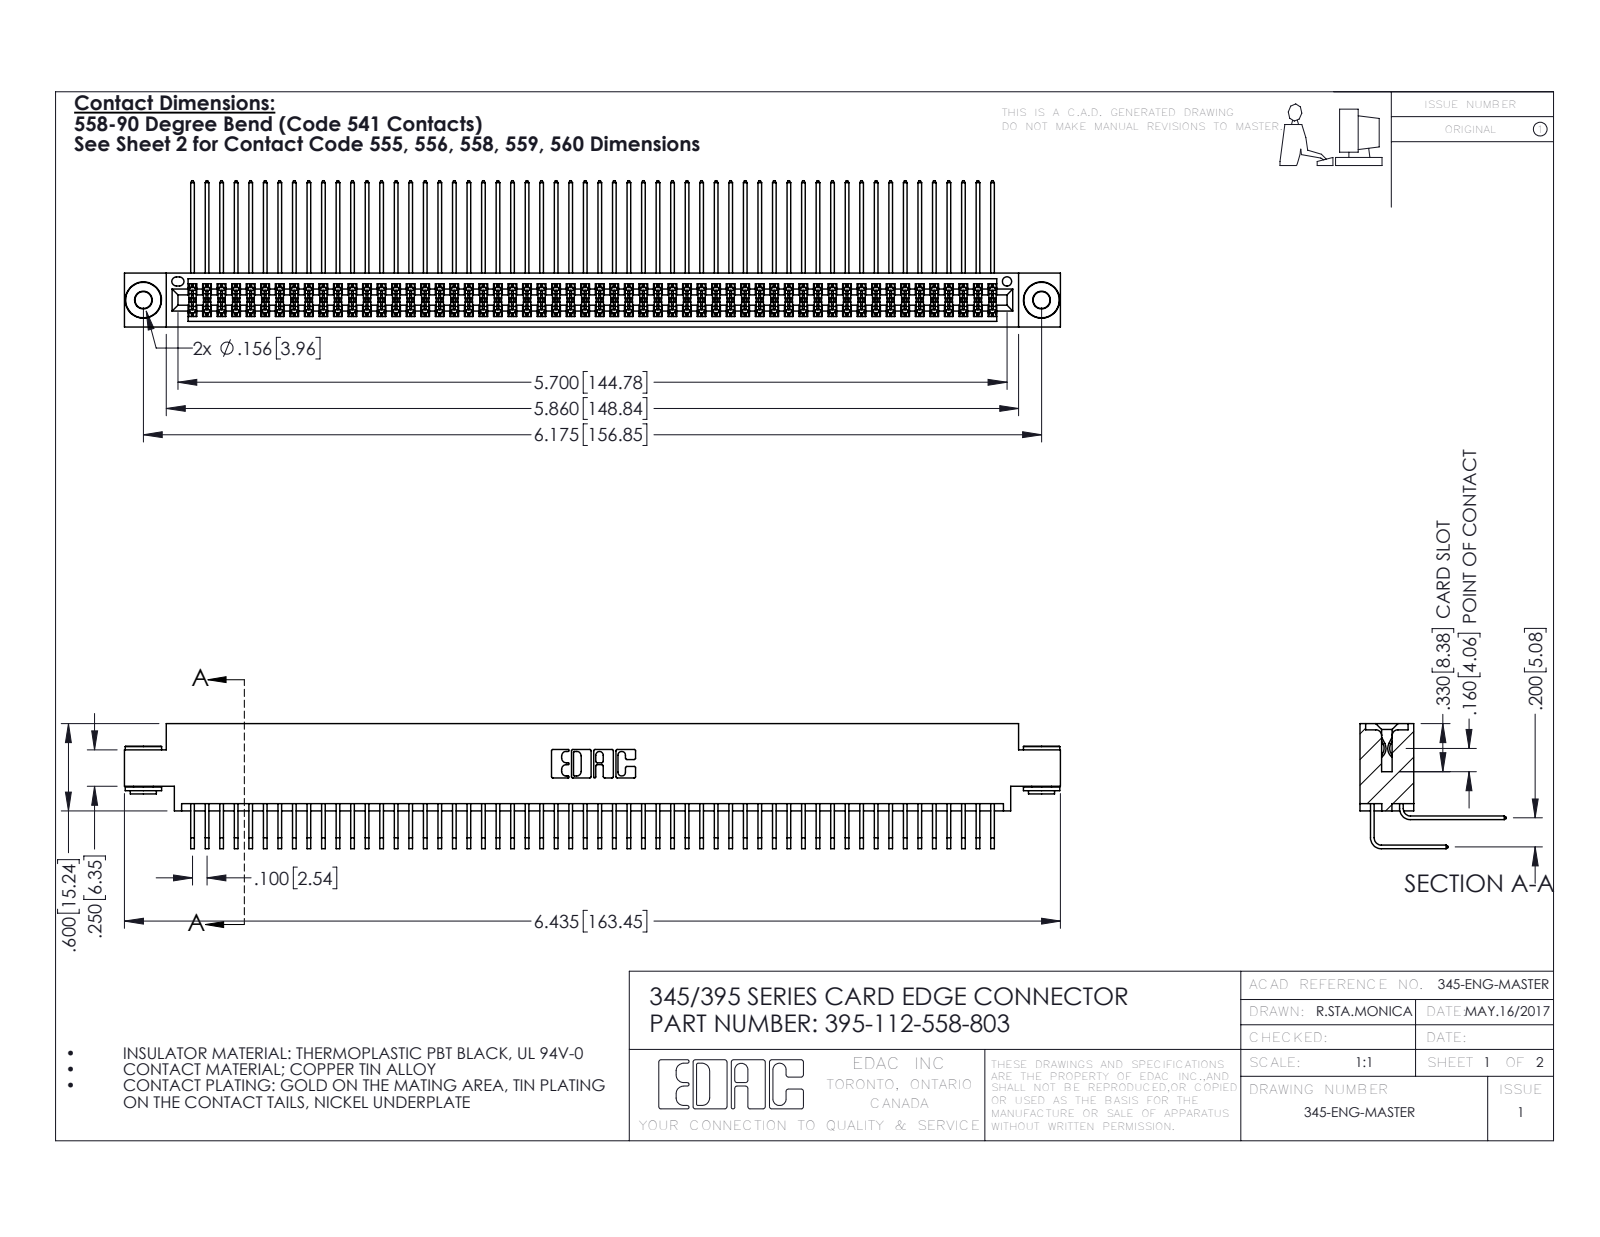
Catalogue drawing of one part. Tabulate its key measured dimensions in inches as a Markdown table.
| quantity | value |
| --- | --- |
| part name | 345-250-002_345-250-002-102; 395-112-558-803; 345-292-001_558 559 Tail - 1; 345 Part_0.170 Offset - 0.156 Dia-TH (+1 more) |
| STEP written by | SolidWorks 2016 (CONFIG_CONTROL_DESIGN) |
| units | inches |
| bodies | 115 solids, 5992 faces (4014 planar, 1970 cylindrical, 8 other) |
| overall size | 6.435 × 1.005 × 0.859 |
| volume | 1.011 in³ |
| surface area | 43.61 in² |
| round holes (diameter × count) | 0.116 × 2, 0.156 × 2, 0.064 × 1 |
| round bosses / shafts (diameter × count) | 0.25 × 2, 0.18 × 2, 0.136 × 2 |
| partial cylindrical surfaces (radius × count) | 0.006 × 169, 0.01 × 22, 0.007 × 6, 0.031 × 6, 0.026 × 3, 0.014 × 2, 0.019 × 2, 0.022 × 2 |
| main face-to-face distances | 0.072, 0.298, 0.2, 0.37, 0.098, 0.272, 0.025, 0.225, 0.175, 0.025 |
| hole center spacings | 0.27, 5.939, 6.175 |
